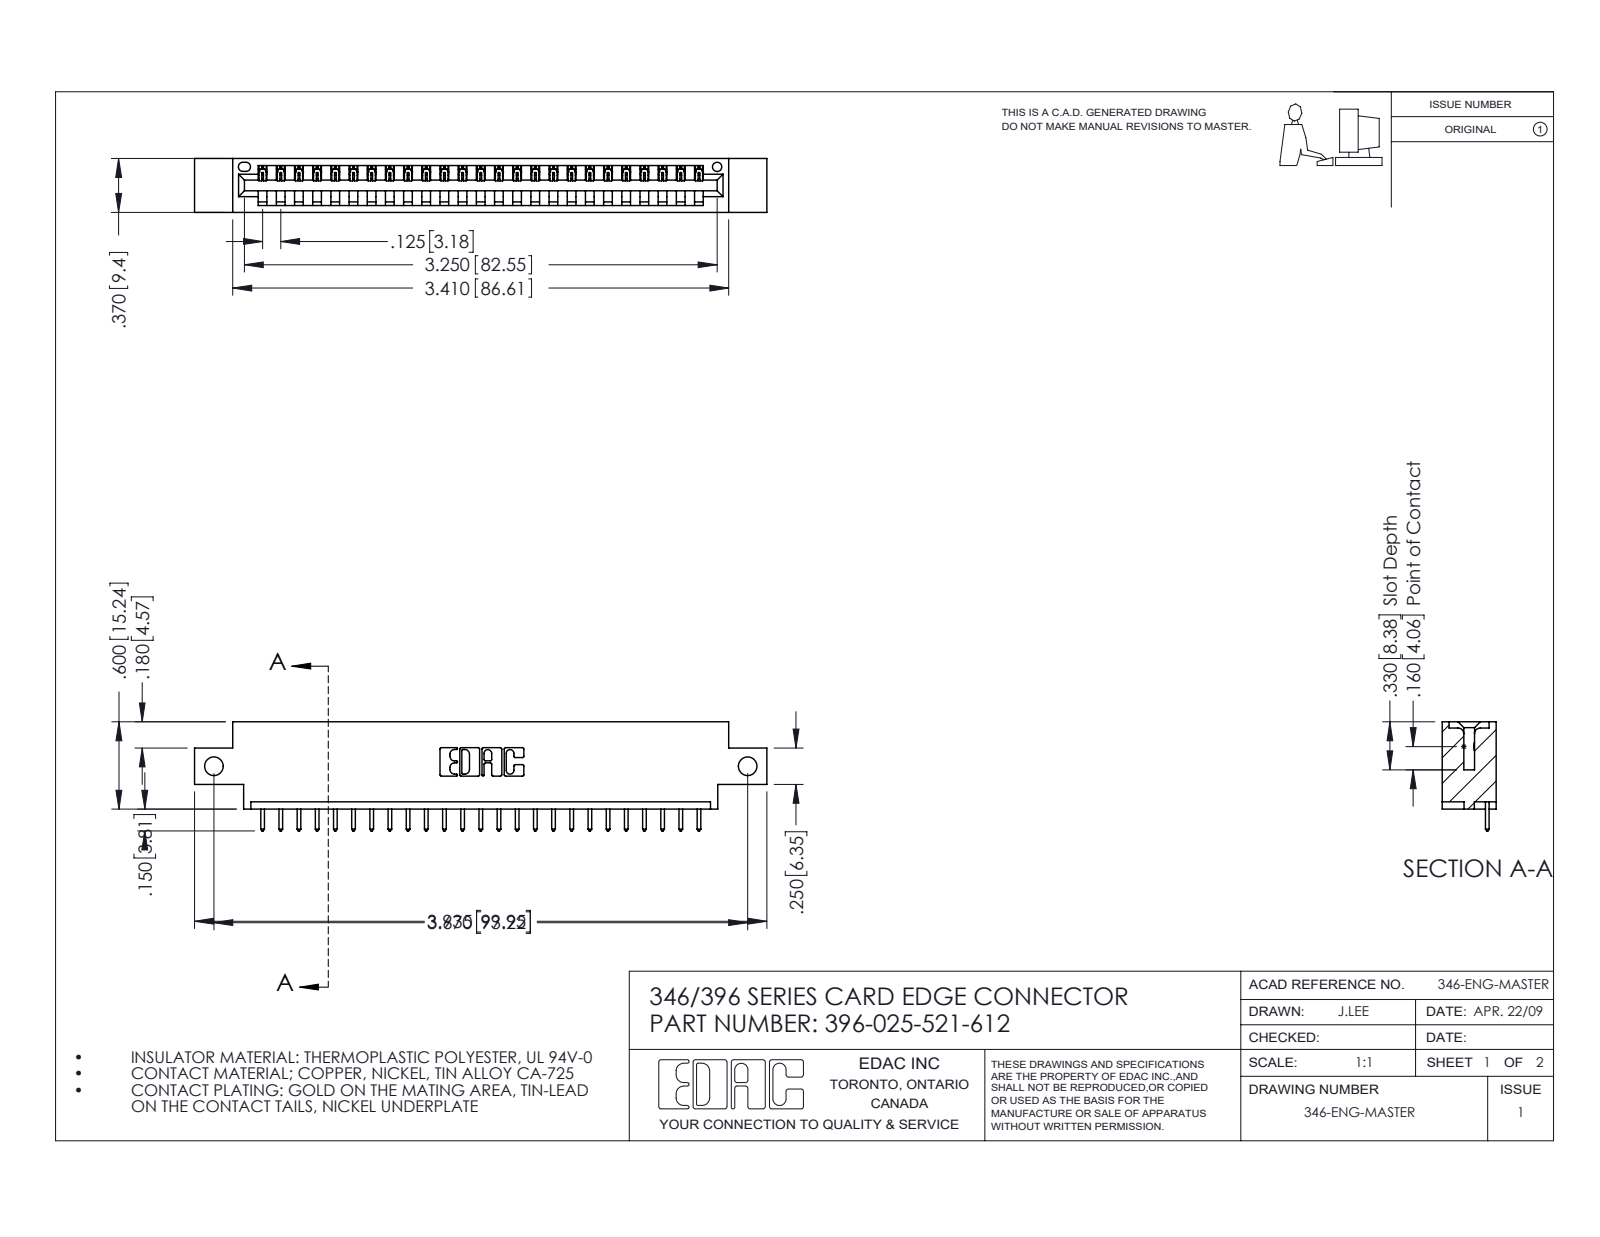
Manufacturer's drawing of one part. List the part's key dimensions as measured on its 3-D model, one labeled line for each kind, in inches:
Part name (STEP PRODUCT): 396-025-521-612; 346 Part_0.170 Offset - Side Mount; 345-292-001_345-293-121
STEP written by: SolidWorks 2016 (CONFIG_CONTROL_DESIGN)
Units: inches
Bodies: 26 solids, 1576 faces (1080 planar, 496 cylindrical, 0 other)
Overall size (bounding box): 3.935 × 0.75 × 0.37
Volume: 0.558 in³ · Surface area: 17 in²
Round holes (diameter × count): ⌀0.128 ×2, ⌀0.064 ×1
Partial cylindrical surfaces — rounded edges, fillets, slot ends (radius × count): R0.006 ×50, R0.01 ×50, R0.01 ×22, R0.007 ×6, R0.031 ×6, R0.026 ×3, R0.031 ×2, R0.04 ×2
Main face-to-face distances: 0.048, 0.322, 0.37, 0.25, 0.072, 0.298, 0.025, 0.148, 0.222, 0.1
Hole centre spacings: 3.67
